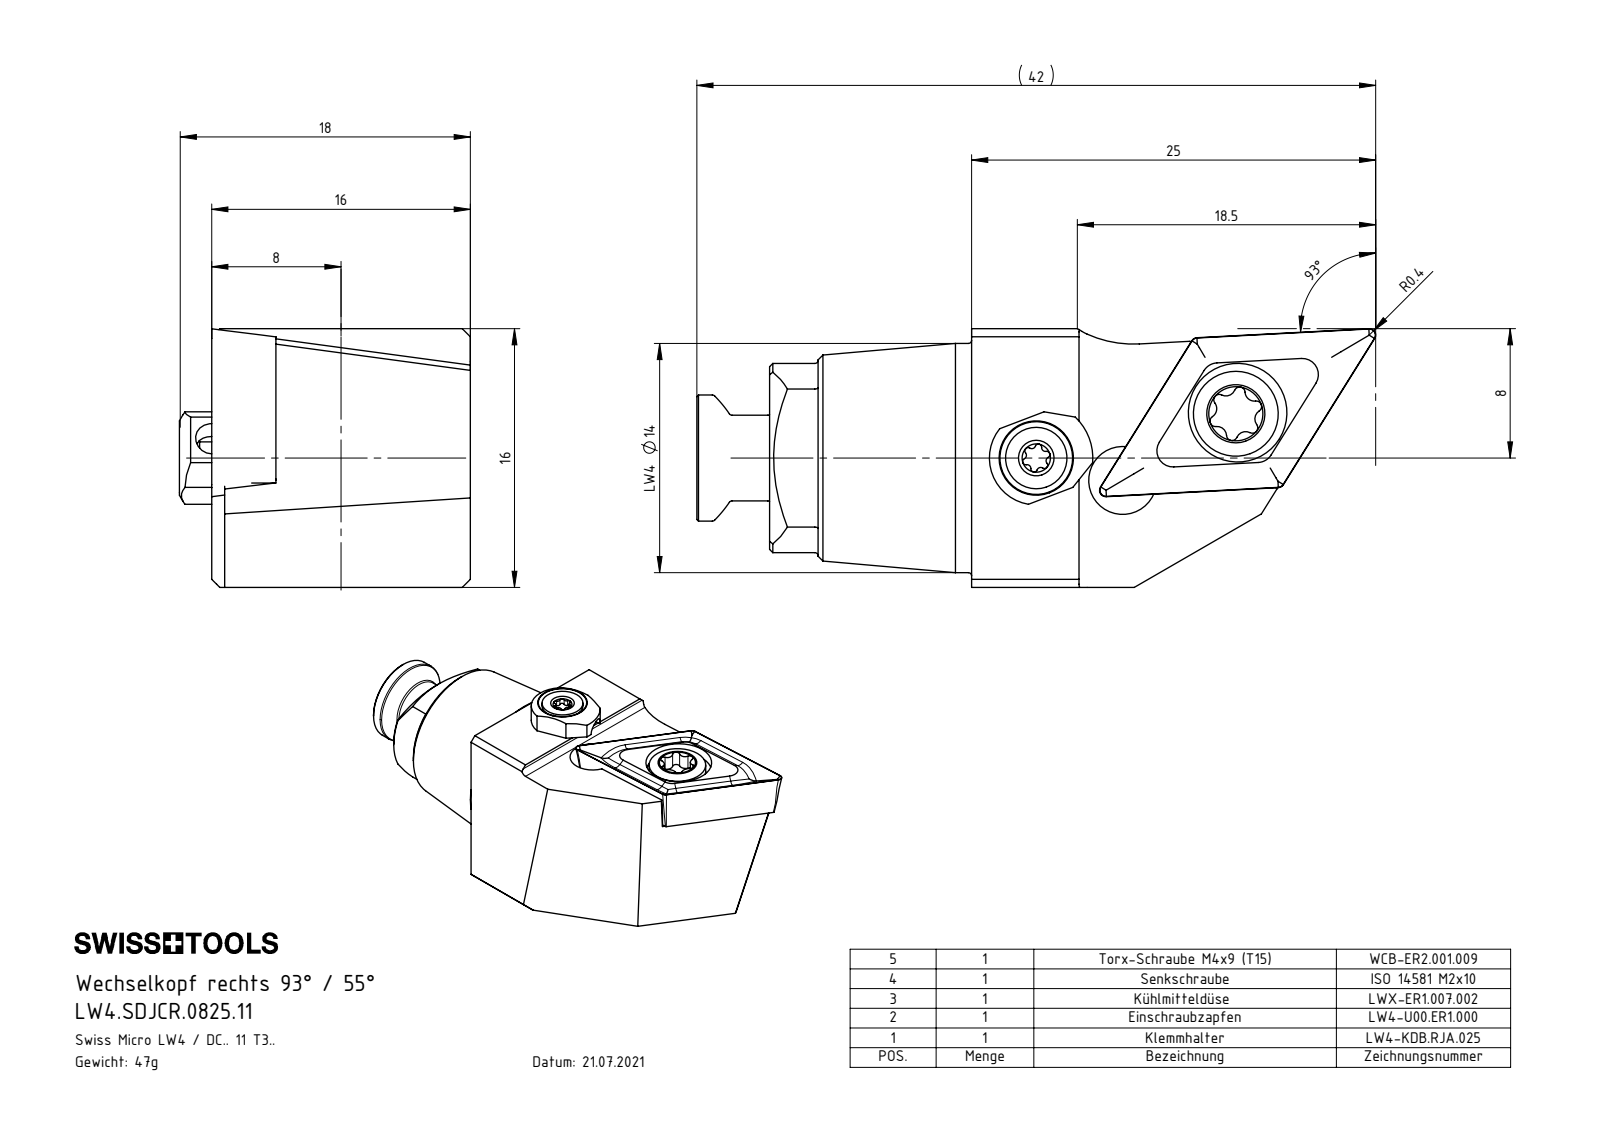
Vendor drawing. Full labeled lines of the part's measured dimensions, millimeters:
Part name (STEP PRODUCT): LW4-KDB.RJA.025_A; LWX-ER1.007.002; DCMT11T304; WCB-ER2.001.009_A (+3 more)
STEP written by: SolidWorks 2017 (AUTOMOTIVE_DESIGN)
Units: millimetres
Bodies: 6 solids, 193 faces (69 planar, 53 cylindrical, 71 other)
Overall size (bounding box): 42.01 × 18 × 16
Volume: 5 756 mm³ · Surface area: 3 668 mm²
Round holes (diameter × count): ⌀2 ×2, ⌀1.6 ×1, ⌀2.5 ×1, ⌀3 ×1, ⌀3.3 ×1, ⌀4.2 ×1, ⌀4.4 ×1, ⌀5.5 ×1, ⌀6.1 ×1
Round bosses / shafts (diameter × count): ⌀14.17 ×1, ⌀7.7 ×1, ⌀6 ×1, ⌀5.3 ×1, ⌀5.25 ×1, ⌀5 ×1, ⌀4 ×1, ⌀3.8 ×1
Partial cylindrical surfaces — rounded edges, fillets, slot ends (radius × count): R0.2 ×8, R0.24 ×6, R0.34 ×6, R0.59 ×6, R0.5 ×1, R1 ×1, R2.9 ×1, R3.5 ×1
Main face-to-face distances: 16, 12.03, 3.97, 15.2, 3.17, 0.8, 7.5, 2, 3, 12.5
Hole centre spacings: 5.53, 8.13, 8.25, 12.65, 12.77
